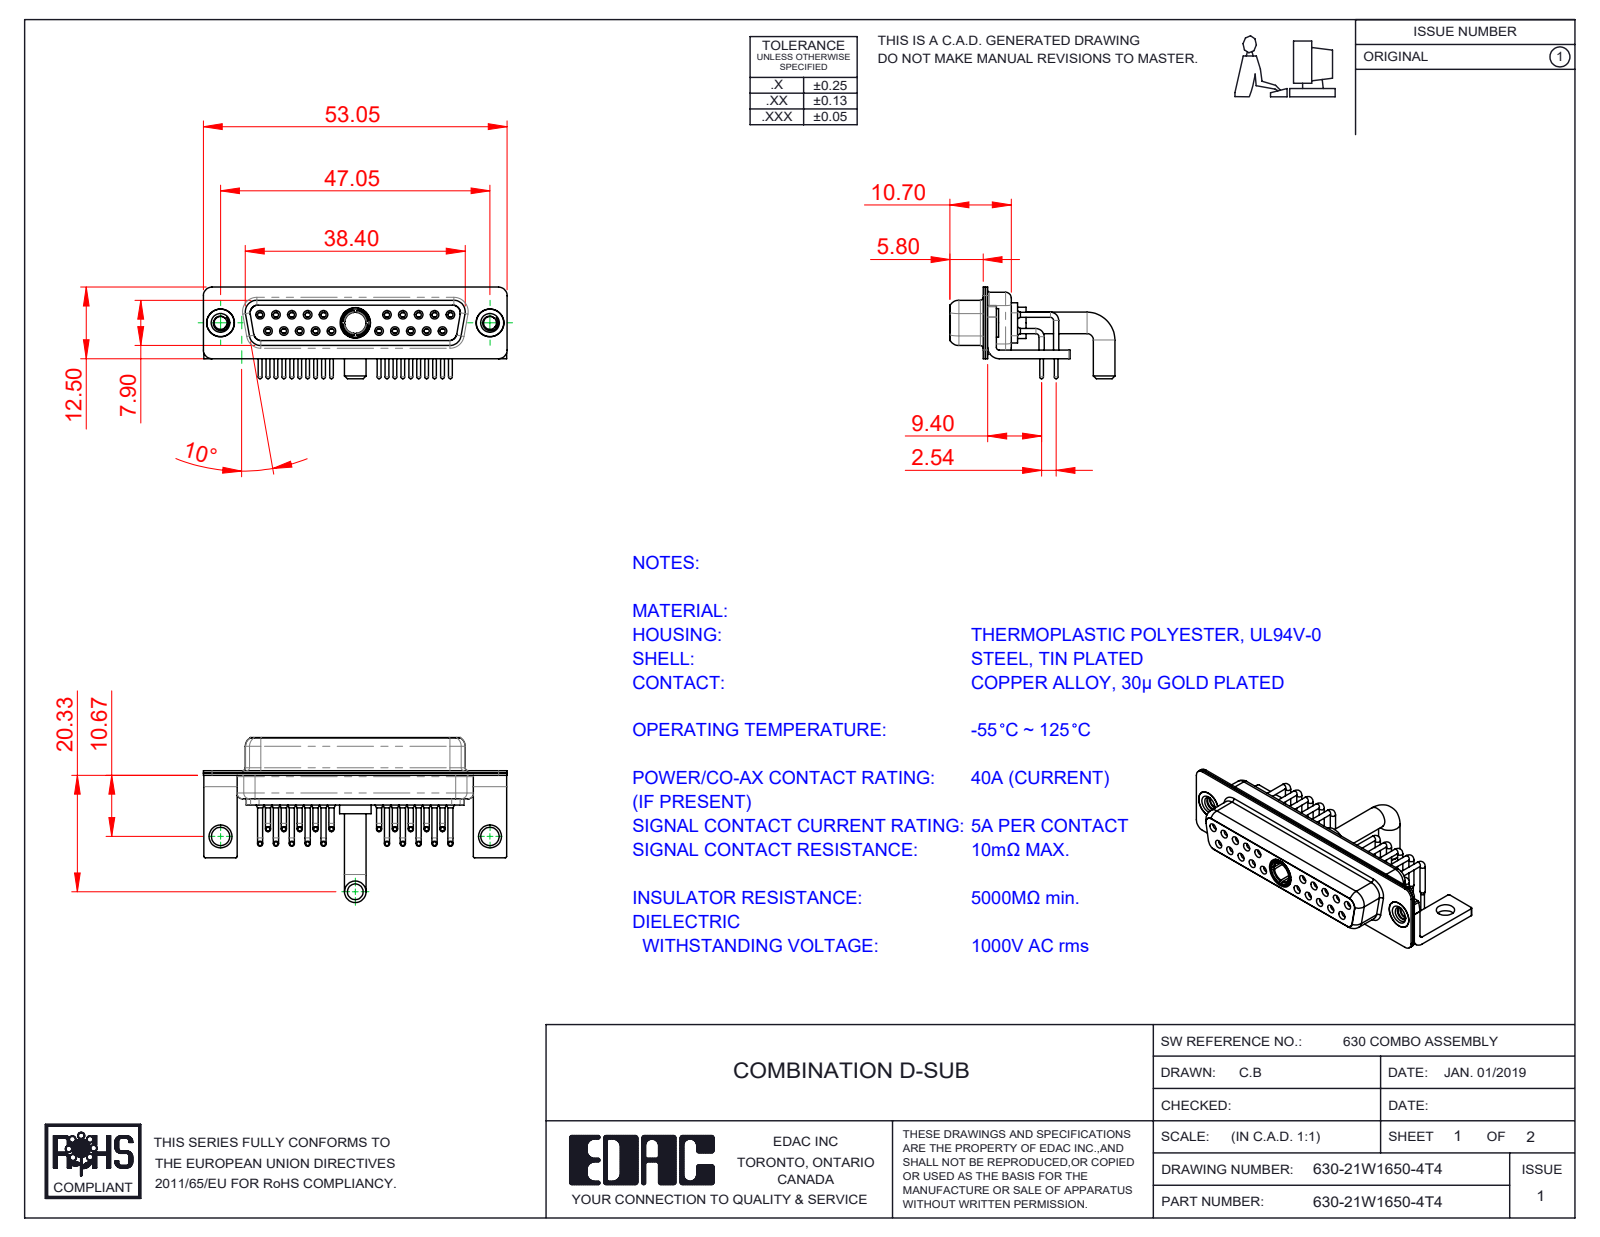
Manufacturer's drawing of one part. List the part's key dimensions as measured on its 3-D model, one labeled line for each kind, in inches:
Part name (STEP PRODUCT): 630Combo Contact Row 1; 630Combo Stabilizer Bracket; 630Combo Shell Rear_25 Contacts; 630-21W1650-4T4 (+5 more)
STEP written by: SolidWorks 2020 (CONFIG_CONTROL_DESIGN)
Units: inches
Bodies: 29 solids, 1457 faces (416 planar, 640 cylindrical, 401 other)
Overall size (bounding box): 2.089 × 1.134 × 0.63
Volume: 0.271 in³ · Surface area: 15.6 in²
Round holes (diameter × count): ⌀0.035 ×20, ⌀0.043 ×20, ⌀0.059 ×20, ⌀0.079 ×20, ⌀0.063 ×10, ⌀0.067 ×10, ⌀0.191 ×3, ⌀0.089 ×2, ⌀0.126 ×2, ⌀0.157 ×2, ⌀0.159 ×2, ⌀0.146 ×1
Round bosses / shafts (diameter × count): ⌀0.035 ×20, ⌀0.026 ×20, ⌀0.063 ×10, ⌀0.197 ×2, ⌀0.195 ×2, ⌀0.189 ×2, ⌀0.148 ×2, ⌀0.217 ×1
Partial cylindrical surfaces — rounded edges, fillets, slot ends (radius × count): R0.01 ×16, R0.059 ×16, R0.079 ×13, R0.053 ×8, R0.063 ×8, R0.02 ×5, R0.024 ×4, R0.026 ×4
Main face-to-face distances: 0.016, 0.018, 0.055, 0.333, 0.071, 0.031, 0.35, 0.244, 0.278, 0.059
Hole centre spacings: 0.124, 0.109, 0.218, 0.327, 0.198, 0.763, 0.826, 0.872
